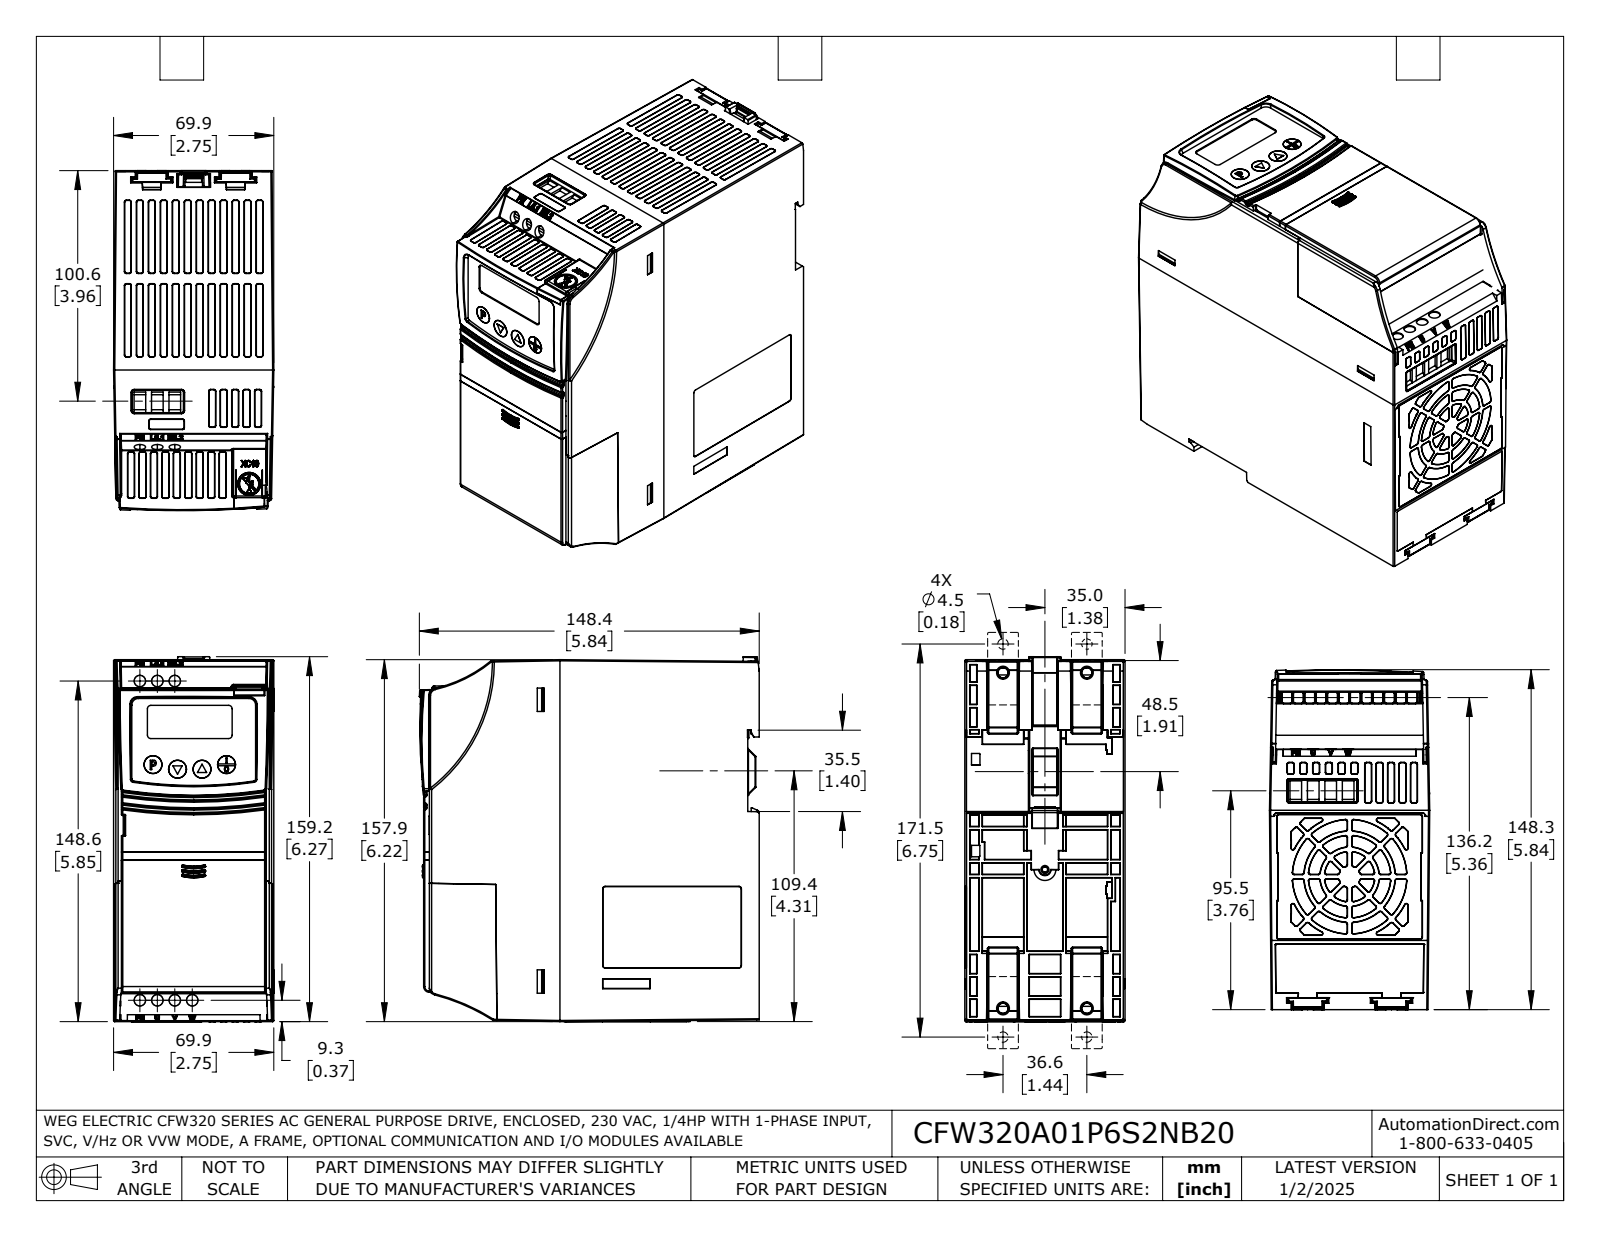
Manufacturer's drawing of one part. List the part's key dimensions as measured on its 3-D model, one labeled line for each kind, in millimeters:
Part name (STEP PRODUCT): CFW320A01P6S2NB20
STEP written by: SolidWorks 2021 (AUTOMOTIVE_DESIGN)
Units: millimetres
Bodies: 6 solids, 3715 faces (1587 planar, 853 cylindrical, 1275 other)
Overall size (bounding box): 159.2 × 148.4 × 70
Volume: 249 700 mm³ · Surface area: 199 400 mm²
Round holes (diameter × count): ⌀5 ×3
Partial cylindrical surfaces — rounded edges, fillets, slot ends (radius × count): R0.3 ×327, R0.5 ×150, R1 ×13, R0.8 ×5, R3 ×3, R0.3 ×2, R2.5 ×1, R3.2 ×1
Main face-to-face distances: 1.8, 1.4, 0.5, 1.3, 152.4, 135.4, 134, 141.5, 140.1, 6.1
Hole centre spacings: 7.6, 15.2
